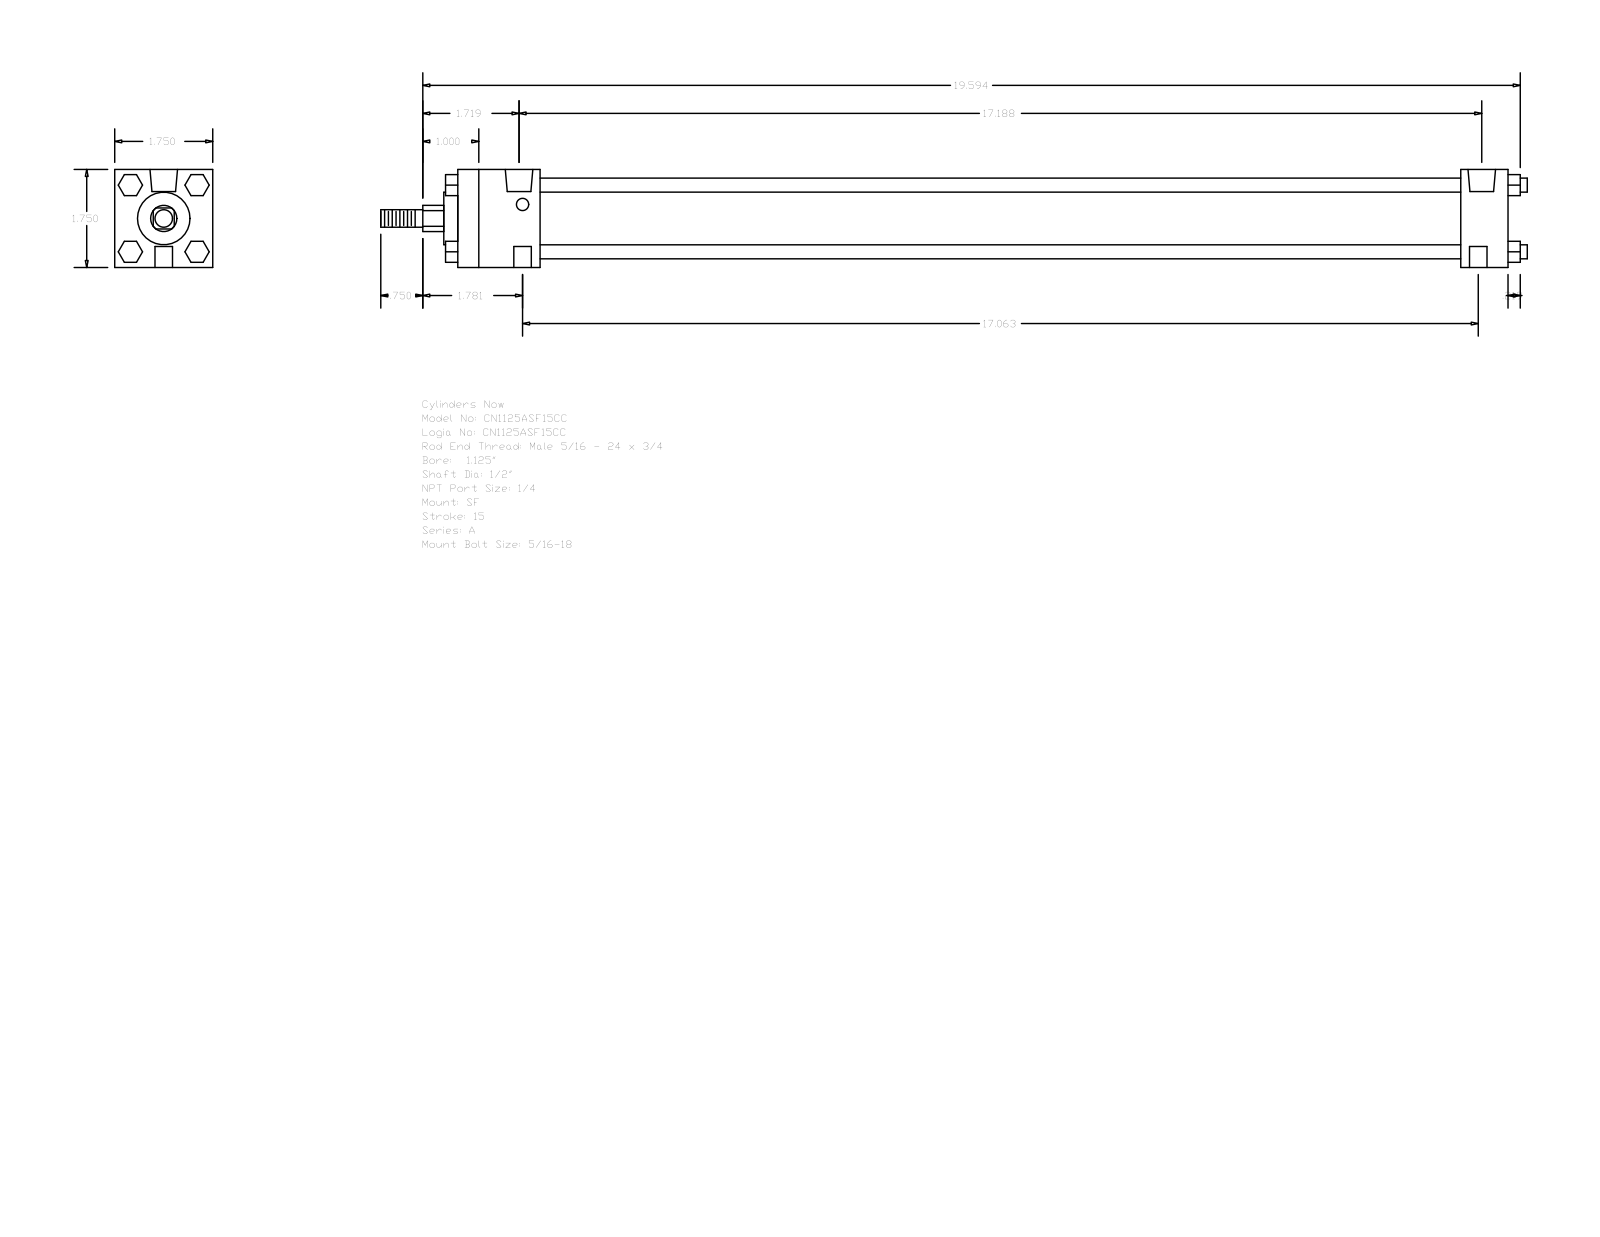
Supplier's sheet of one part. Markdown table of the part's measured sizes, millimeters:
| quantity | value |
| --- | --- |
| part name | A_SF__0112_0.5 |
| STEP written by | GSSL Pune (CONFIG_CONTROL_DESIGN) |
| units | millimeters |
| bodies | 0 solids, 120 faces (92 planar, 28 cylindrical, 0 other) |
| overall size | 519.91 × 44.45 × 44.45 |
| round holes (diameter × count) | 5.56 × 2, 7.94 × 2, 12.49 × 2 |
| round bosses / shafts (diameter × count) | 6.35 × 4, 31.88 × 1, 23.81 × 1, 12.7 × 1, 7.94 × 1 |
| partial cylindrical surfaces (radius × count) | 5.94 × 1 |
| main face-to-face distances | 44.46, 476.24, 454.81, 21.43, 37.3, 417.51, 438.94, 9.53, 5.59, 5.56 |
| hole center spacings | 433.39, 1.58, 1.59, 434.97, 434.98, 436.56 |
